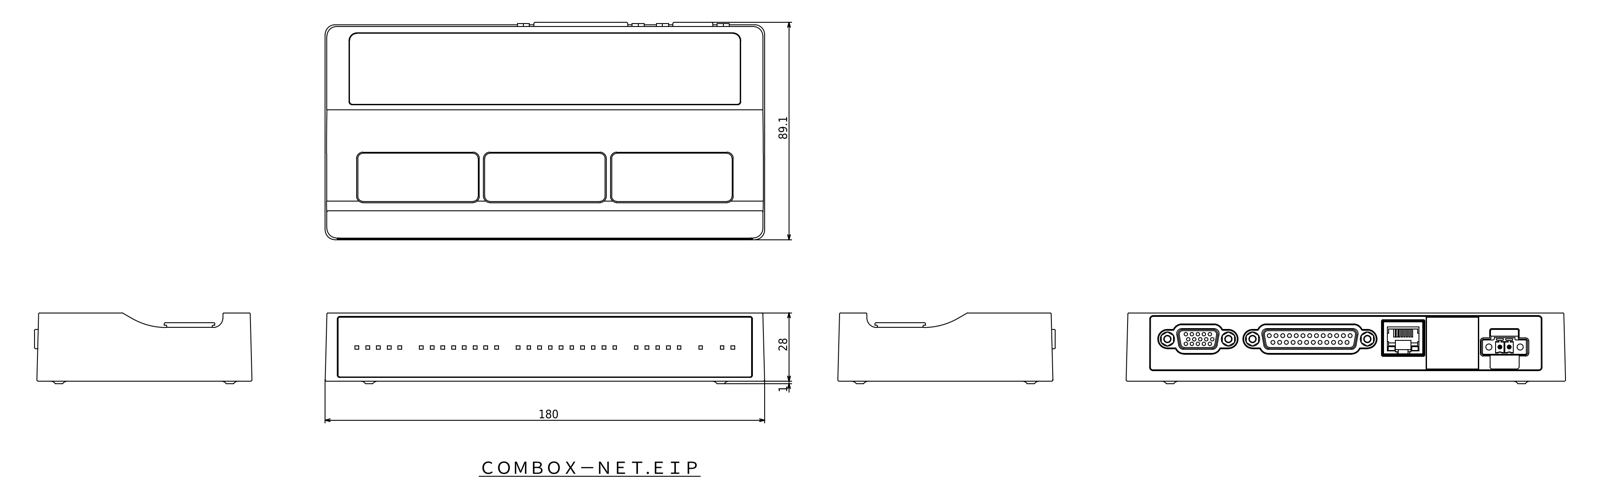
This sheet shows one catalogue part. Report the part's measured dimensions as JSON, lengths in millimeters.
{"part_name": "pxc_1830651_05_MCV-1-5-8-GF-3-81_3D; APTD1608; SML-LXL1210SRGC-TR; DB25 (+8 more)", "step_written_by": "SolidWorks 2021 (CONFIG_CONTROL_DESIGN)", "units": "millimeters", "bodies": {"solids": 237, "faces": 11994, "planar": 9448, "cylindrical": 1807, "other": 739}, "overall_size": [180, 91.35, 29], "volume_mm3": 192734, "surface_area_mm2": 211763, "round_holes": [[0.5, 35], [1.6, 25], [1.4, 15], [2.6, 14], [2.5, 10], [5, 9], [3, 5], [3.5, 5], [4, 5], [7, 5], [1.8, 4], [5.8, 4]], "round_bosses_or_shafts": [[1, 24], [1.2, 8], [1.6, 6], [5.5, 5], [4.6, 5], [3, 5], [2.6, 4], [2, 4]], "partial_cylinders_radius": [[0.5, 116], [0.1, 103], [1, 90], [0.3, 86], [0.2, 55], [0.15, 40], [2, 30], [1.8, 25]], "face_to_face_distances": [3, 11, 1.6, 8, 25, 9.4, 6.4, 0.5, 16.7, 3.5], "hole_center_spacings": [2.46, 2.76, 5.52, 4.92, 8.28, 11.04, 4.67, 13.8]}
